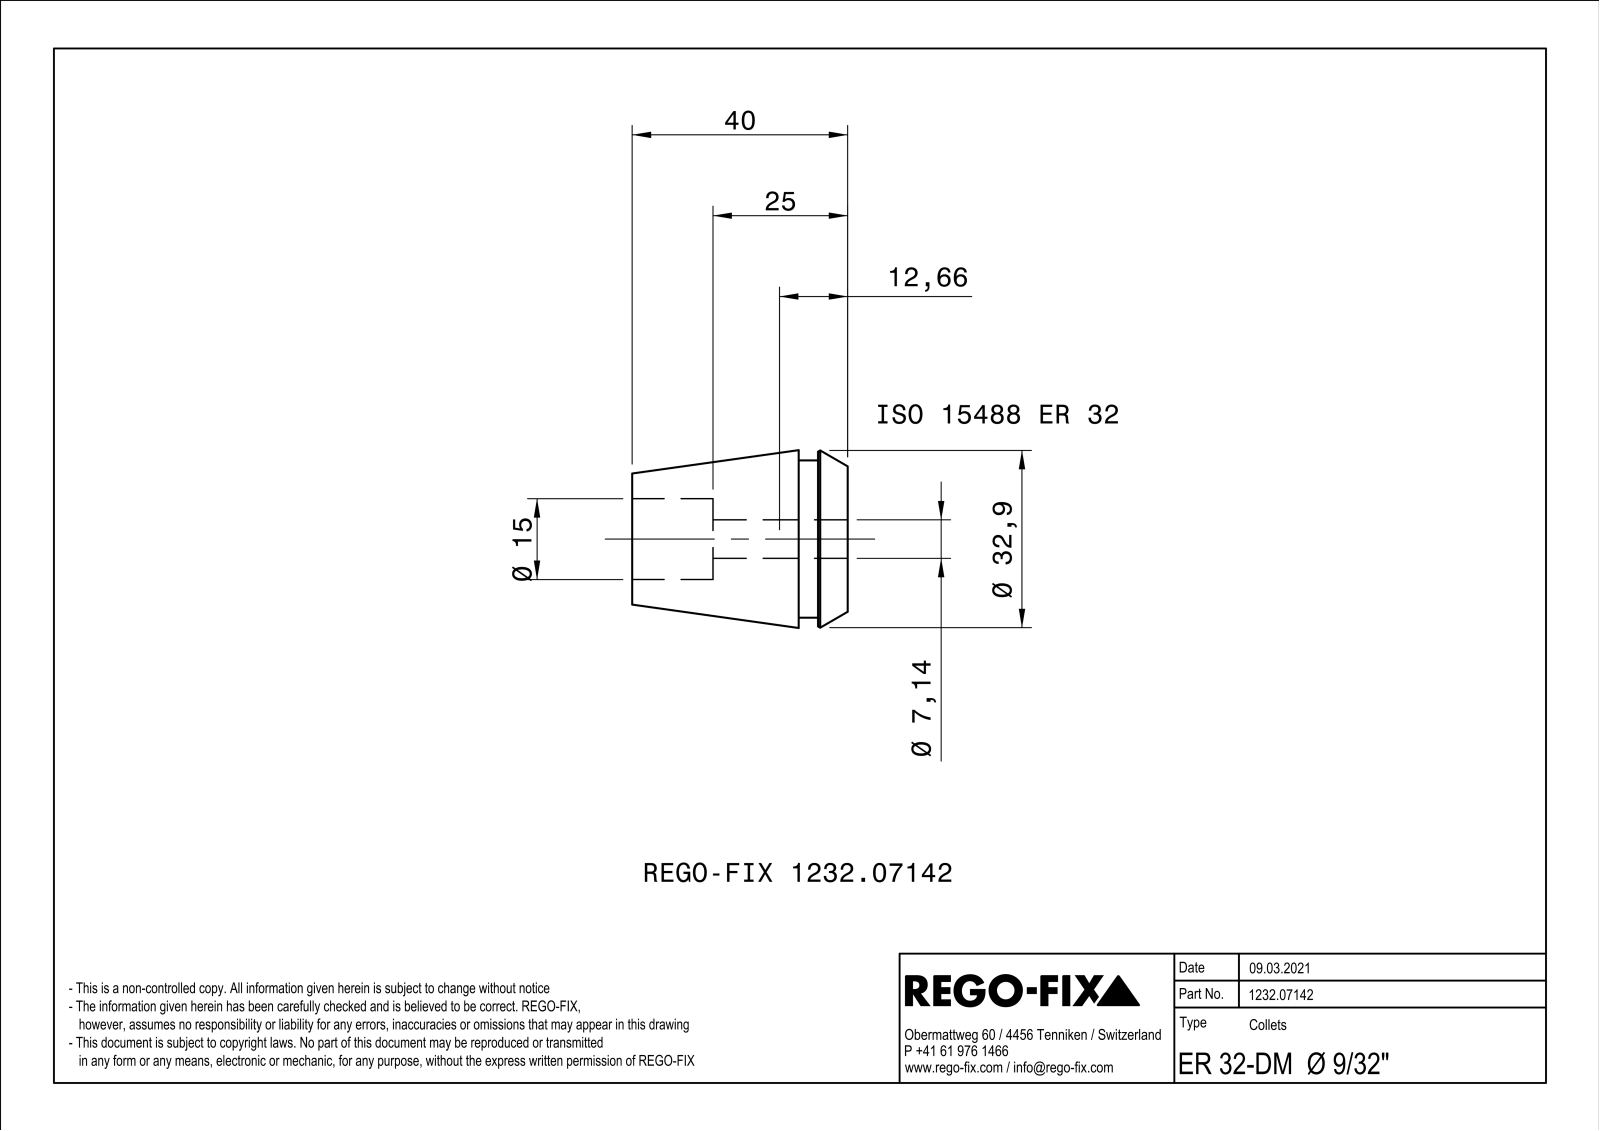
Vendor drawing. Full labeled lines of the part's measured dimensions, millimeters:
Part name (STEP PRODUCT): NOCUT
STEP written by: SIEMENS PLM Software Solid Edge ST10 (AUTOMOTIVE_DESIGN)
Units: millimetres
Bodies: 1 solid, 94 faces (44 planar, 9 cylindrical, 41 other)
Overall size (bounding box): 40 × 32.59 × 32.59
Volume: 19 871 mm³ · Surface area: 9 508 mm²
Round holes (diameter × count): ⌀7.14 ×1, ⌀15 ×1
Round bosses / shafts (diameter × count): ⌀29.2 ×1
Main face-to-face distances: 0.8, 40, 9.1, 30.9, 5.5, 3.6, 34.5, 25, 19.5, 15.9
